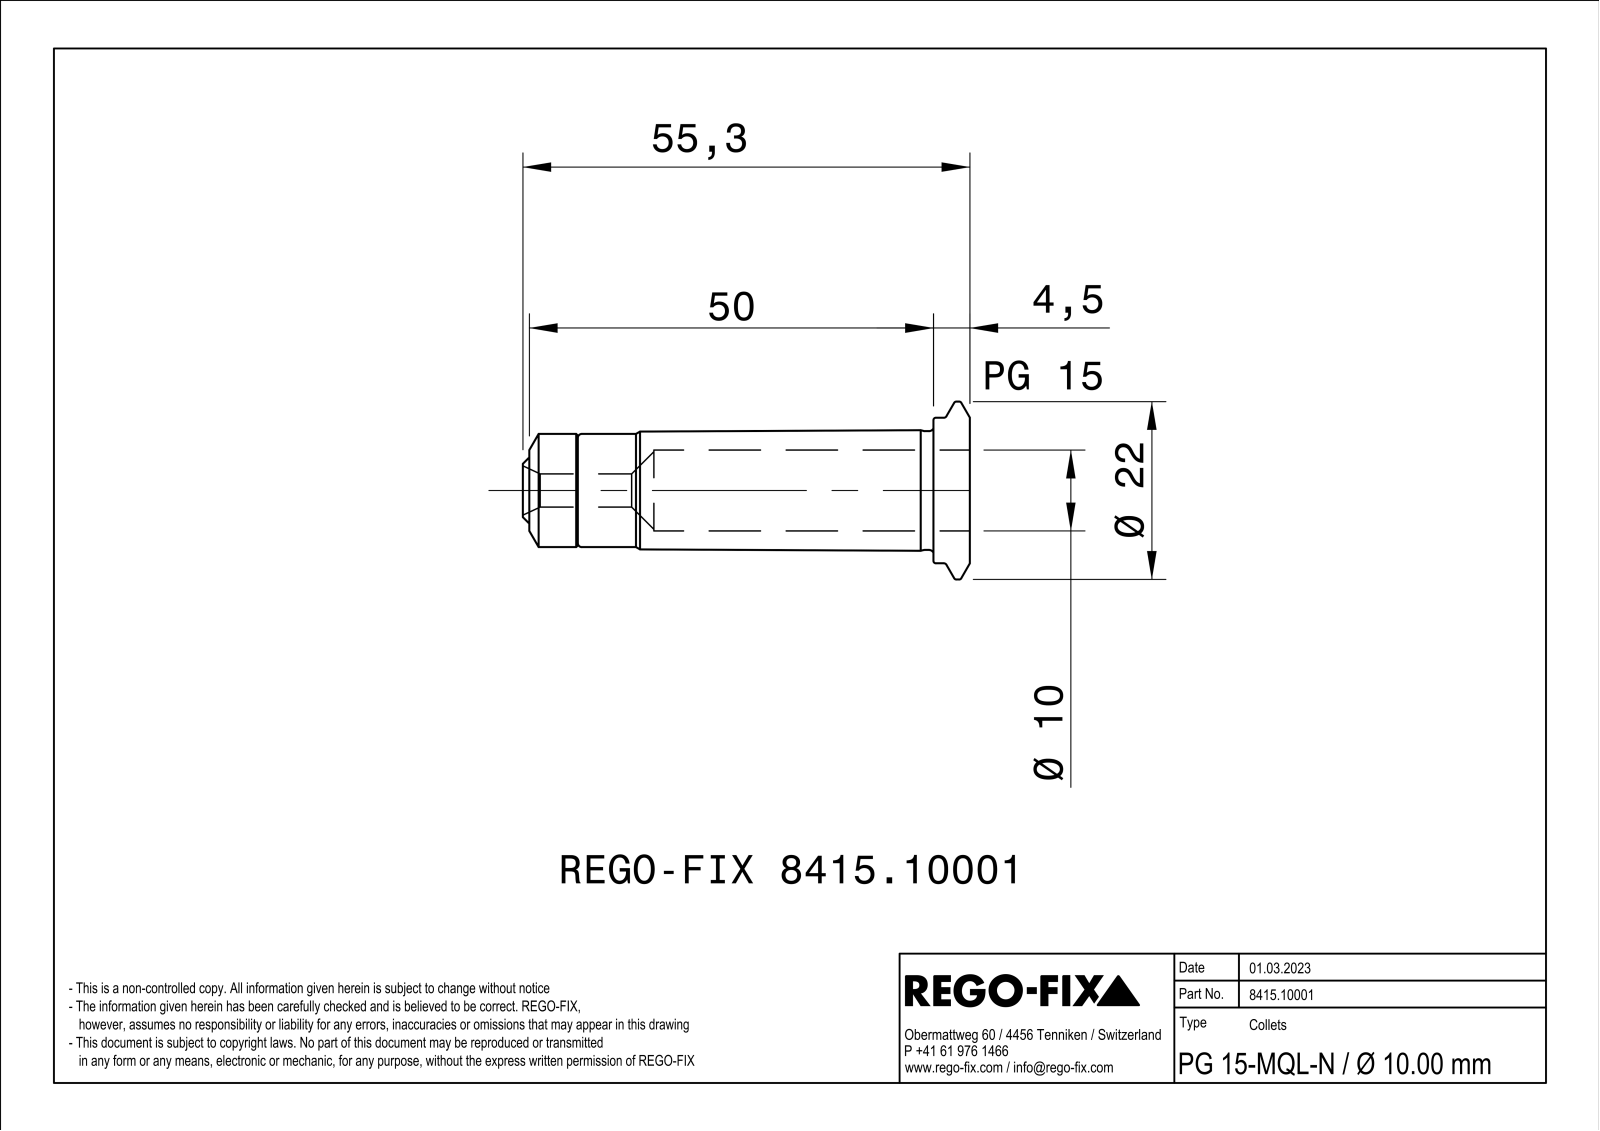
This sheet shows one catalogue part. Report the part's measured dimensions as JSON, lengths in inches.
{"part_name": "NOCUT", "step_written_by": "SIEMENS PLM Software Solid Edge ST10 (AUTOMOTIVE_DESIGN)", "units": "inches", "bodies": {"solids": 2, "faces": 76, "planar": 15, "cylindrical": 17, "other": 44}, "overall_size": [2.177, 0.866, 0.866], "volume_in3": 0.393, "surface_area_in2": 8.944, "round_holes": [[0.161, 1], [0.394, 1], [0.43, 1], [0.48, 1]], "round_bosses_or_shafts": [[0.866, 1], [0.709, 1], [0.579, 1], [0.551, 1], [0.535, 1], [0.315, 1]], "face_to_face_distances": [0.039, 1.909, 0.236, 2.146, 1.673, 0.472, 1.539, 0.134, 0.37, 0.607]}
